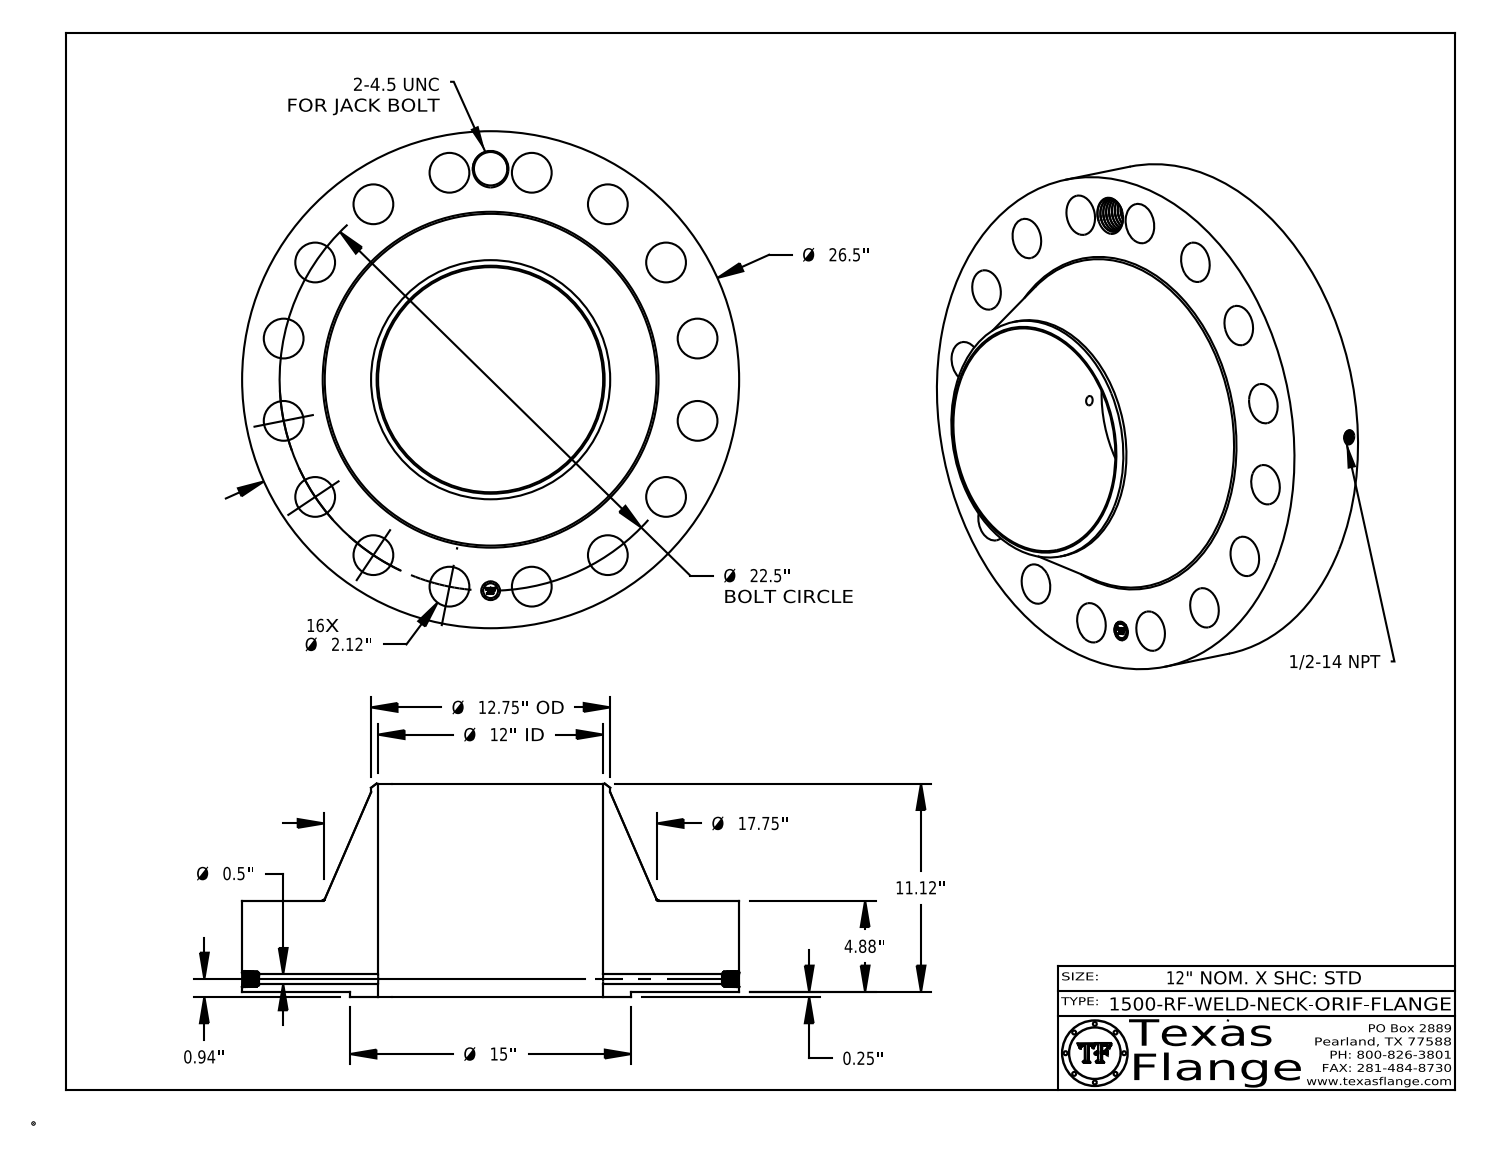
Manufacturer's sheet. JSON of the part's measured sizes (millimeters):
{"part_name": "1500-RF-WELD-NECK", "step_written_by": "CATIA V5 STEP AP214 (AUTOMOTIVE_DESIGN)", "units": "millimeters", "bodies": {"solids": 1, "faces": 827, "planar": 369, "cylindrical": 124, "other": 334}, "overall_size": [673.1, 673.1, 288.8], "volume_mm3": 37360000, "surface_area_mm2": 1539000, "round_holes": [[53.8, 16], [12.7, 1], [17.1, 1], [25.4, 1], [45.2, 1], [304.8, 1]], "round_bosses_or_shafts": [[1.5, 8], [673.1, 1], [381, 1], [323.9, 1], [20, 1]], "face_to_face_distances": [124, 6.4, 130.3, 288.8, 282.4, 158.5, 129.9, 123.6, 0.4, 158.9], "hole_center_spacings": [285.8, 218.7, 404.1, 528, 317.5, 475.2, 560.5, 111.5]}
